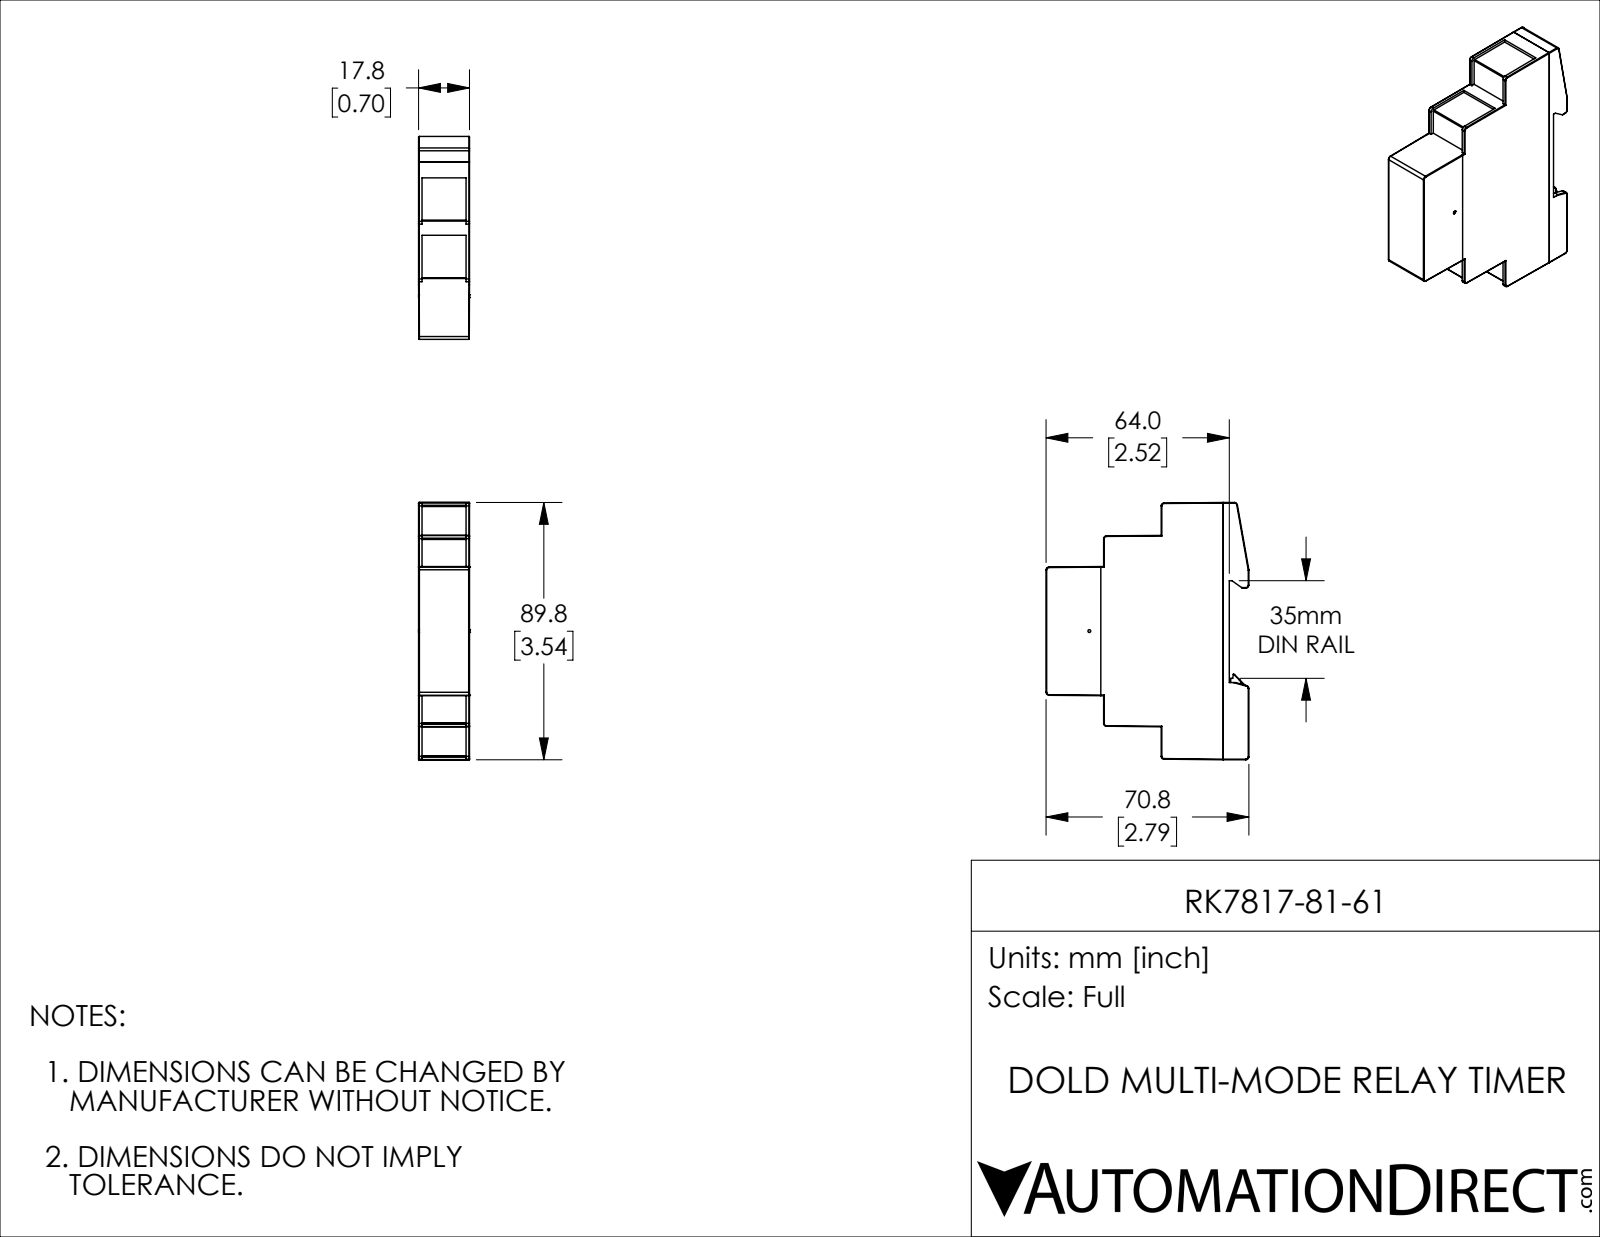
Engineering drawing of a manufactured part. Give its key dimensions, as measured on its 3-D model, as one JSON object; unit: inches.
{"part_name": "RK7817-81-61", "step_written_by": "SolidWorks 2019 (CONFIG_CONTROL_DESIGN)", "units": "inches", "bodies": {"solids": 3, "faces": 267, "planar": 158, "cylindrical": 85, "other": 24}, "overall_size": [3.535, 2.787, 0.701], "volume_in3": 4.945, "surface_area_in2": 31.16, "round_bosses_or_shafts": [[0.039, 1]], "partial_cylinders_radius": [[0.008, 36], [0.039, 12], [0.004, 9], [0.012, 4], [0.02, 2], [0.011, 1], [0.031, 1], [0.118, 1]], "face_to_face_distances": [0.701, 0.085, 2.52, 2.435, 0.383, 0.446, 0.829, 0.791, 0.835, 0.894]}
